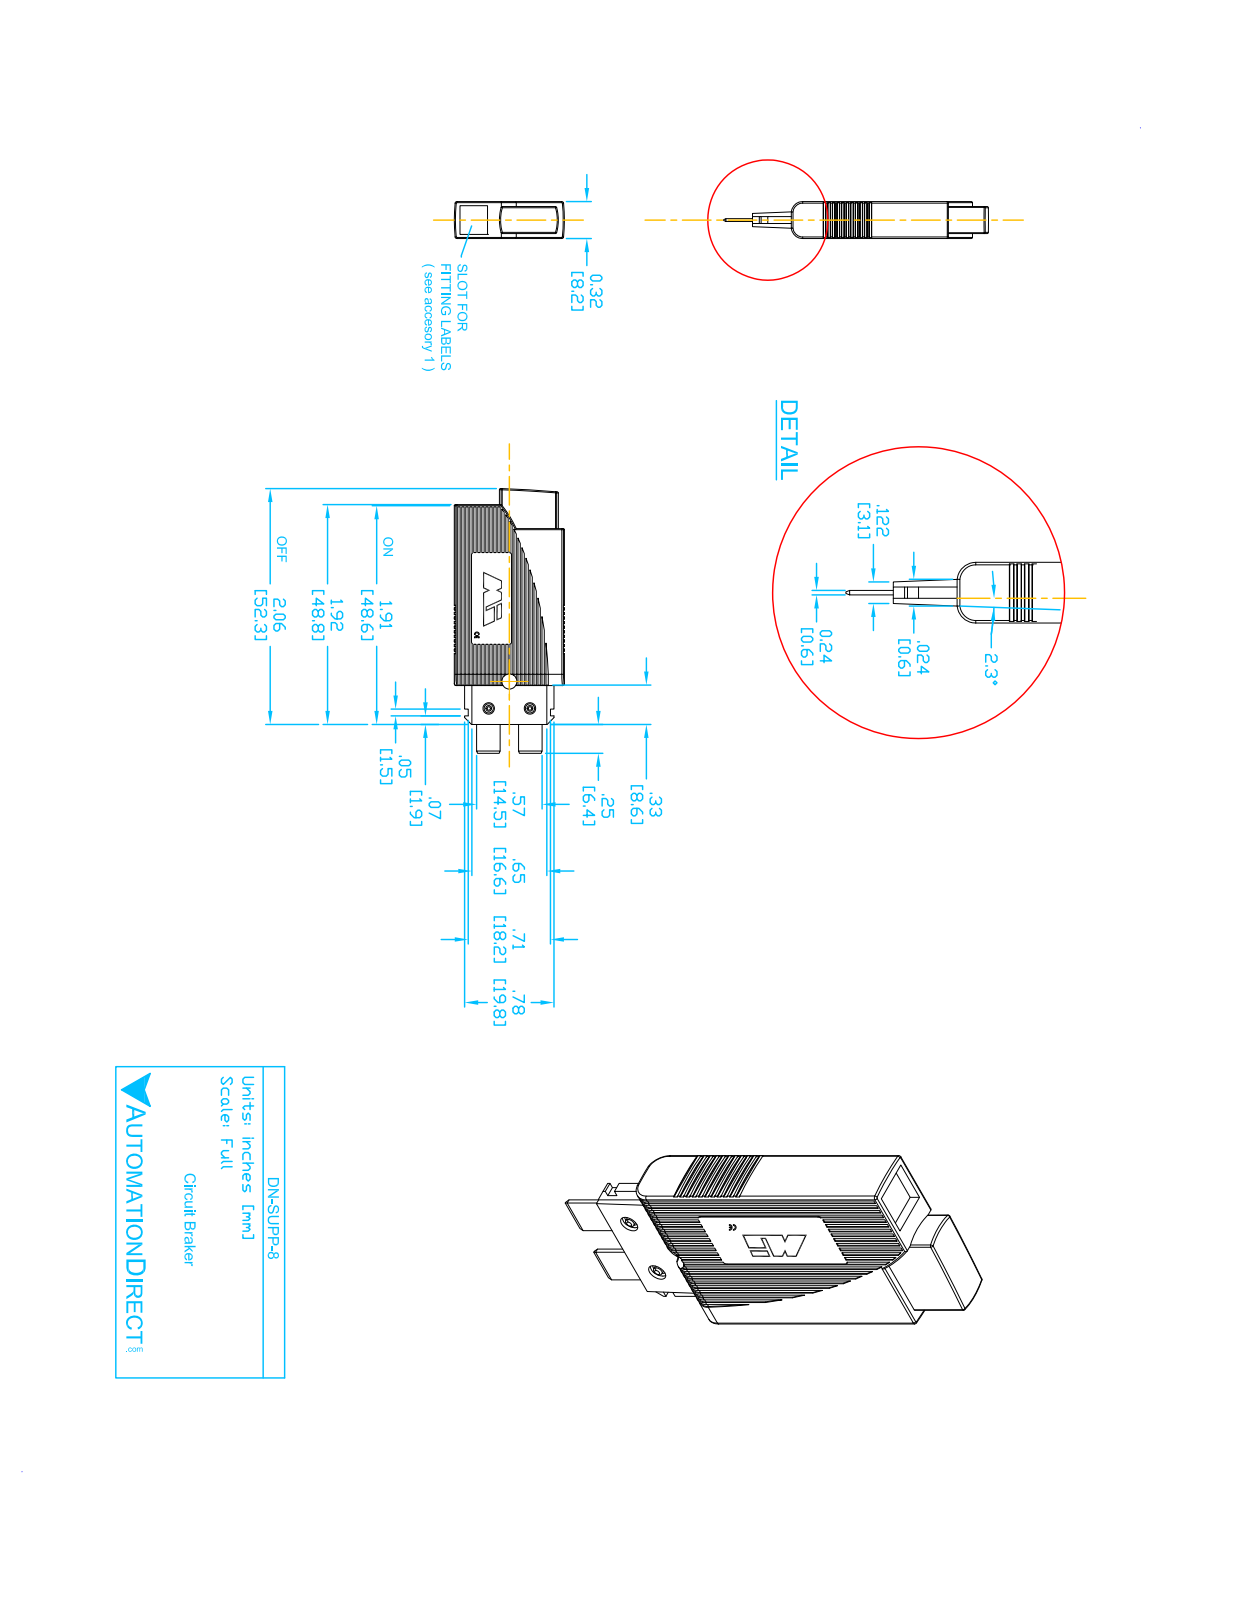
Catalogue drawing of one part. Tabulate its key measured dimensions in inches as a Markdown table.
| quantity | value |
| --- | --- |
| part name | DN-SUPP-8 |
| STEP written by | SolidWorks 2017 (AUTOMOTIVE_DESIGN) |
| units | inches |
| bodies | 1 solid, 95 faces (47 planar, 28 cylindrical, 20 other) |
| overall size | 2.18 × 0.961 × 0.323 |
| volume | 0.505 in³ |
| surface area | 5.231 in² |
| partial cylindrical surfaces (radius × count) | 0.012 × 21, 0.157 × 2, 2.165 × 1, 2.331 × 1, 2.362 × 1 |
| main face-to-face distances | 0.323, 0.961, 0.15, 0.173, 0.031, 0.291, 0.118, 0.142, 0.024, 0.14 |
